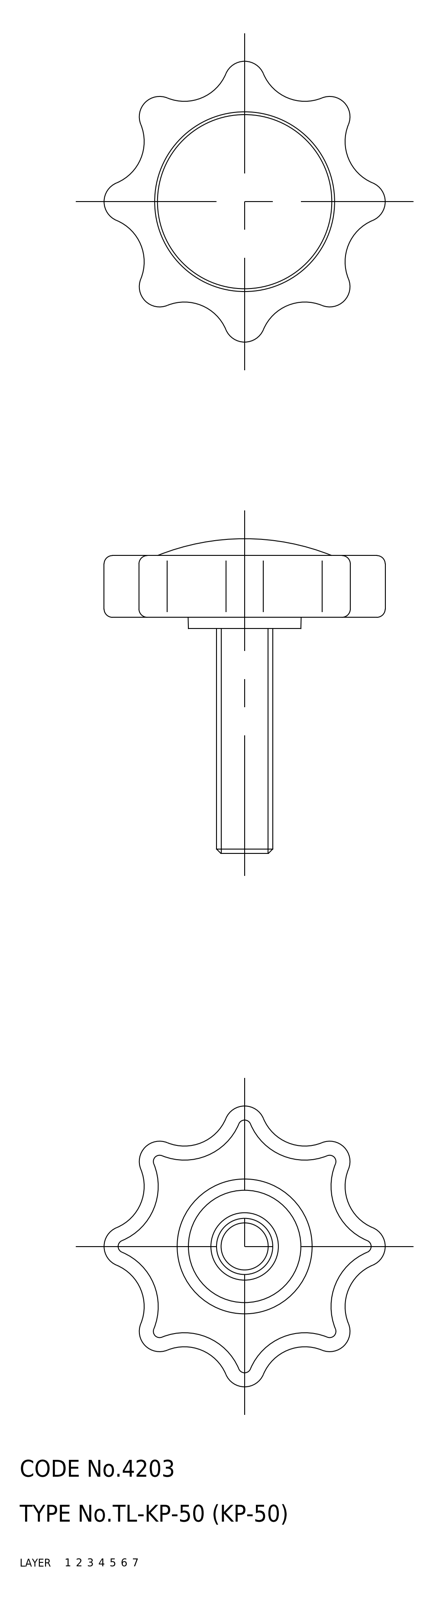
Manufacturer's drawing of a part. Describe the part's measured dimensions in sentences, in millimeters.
The part is named "screw; knob; KP_50_8065_36". Its 3-D file was written by "CADfix (AUTOMOTIVE_DESIGN)". It is 2 solids with 100 faces: 0 planar, 0 cylindrical and 100 other. Overall it measures 56 by 50 by 50 millimeters. Its volume is 15 011 cubic millimeters and its surface area 8 764 square millimeters.
